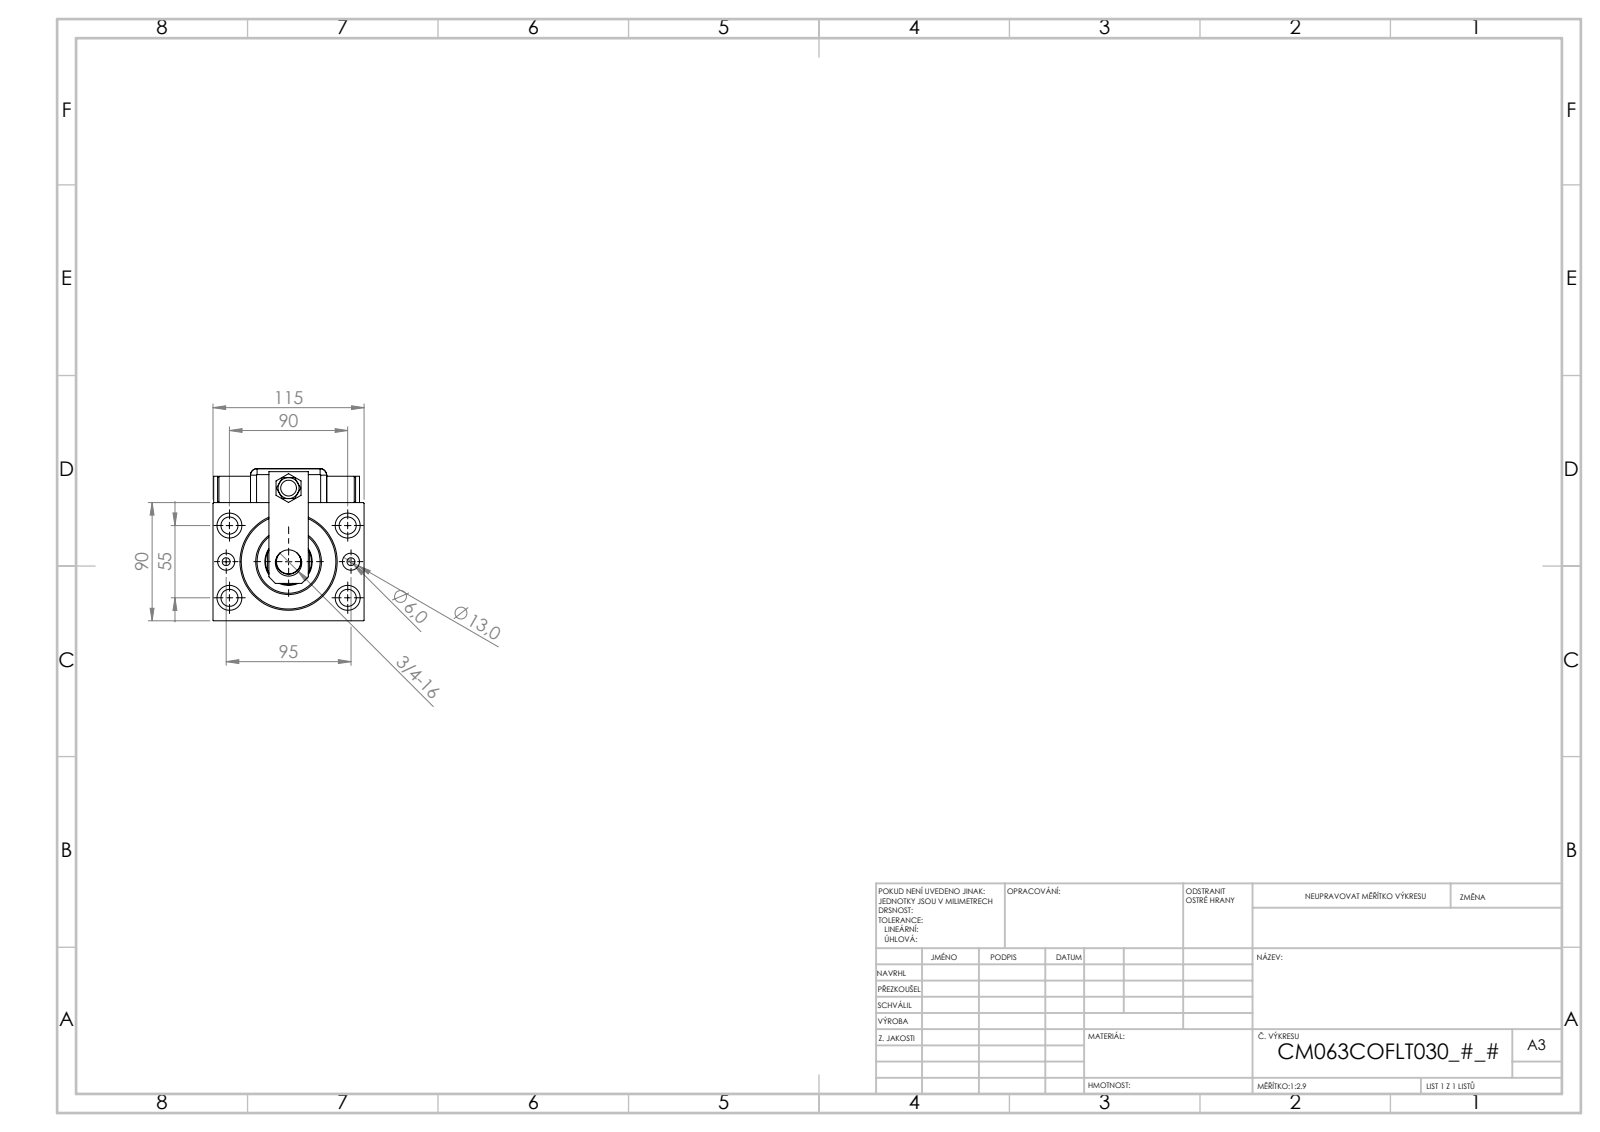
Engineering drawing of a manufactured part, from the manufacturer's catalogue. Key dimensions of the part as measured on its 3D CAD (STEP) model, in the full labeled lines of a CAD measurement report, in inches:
Part name (STEP PRODUCT): KRYT; SWITCH DIM A_G; SWITCH_Q_FRONT_BACK; V450CM_C_VCP (+7 more)
STEP written by: SolidWorks 2019 (CONFIG_CONTROL_DESIGN)
Units: inches
Bodies: 13 solids, 1242 faces (614 planar, 111 cylindrical, 517 other)
Overall size (bounding box): 6.317 × 4.559 × 4.528
Volume: 69.02 in³ · Surface area: 305.9 in²
Round holes (diameter × count): ⌀0.512 ×7, ⌀0.748 ×4, ⌀0.157 ×2, ⌀0.236 ×2, ⌀0.315 ×2, ⌀0.472 ×1, ⌀0.551 ×1, ⌀0.728 ×1, ⌀0.787 ×1, ⌀1.417 ×1, ⌀2.48 ×1, ⌀2.559 ×1
Round bosses / shafts (diameter × count): ⌀0.787 ×3, ⌀0.63 ×2, ⌀0.551 ×2, ⌀0.236 ×2, ⌀1.969 ×1
Partial cylindrical surfaces — rounded edges, fillets, slot ends (radius × count): R0.197 ×9, R0.394 ×1, R0.689 ×1
Main face-to-face distances: 3.543, 0.118, 4.528, 4.252, 3.563, 0.689, 0.531, 0.315, 1.016, 4.559
Hole centre spacings: 1.087, 2.076, 2.097, 3.799, 1.87, 1.87, 2.056, 2.165
